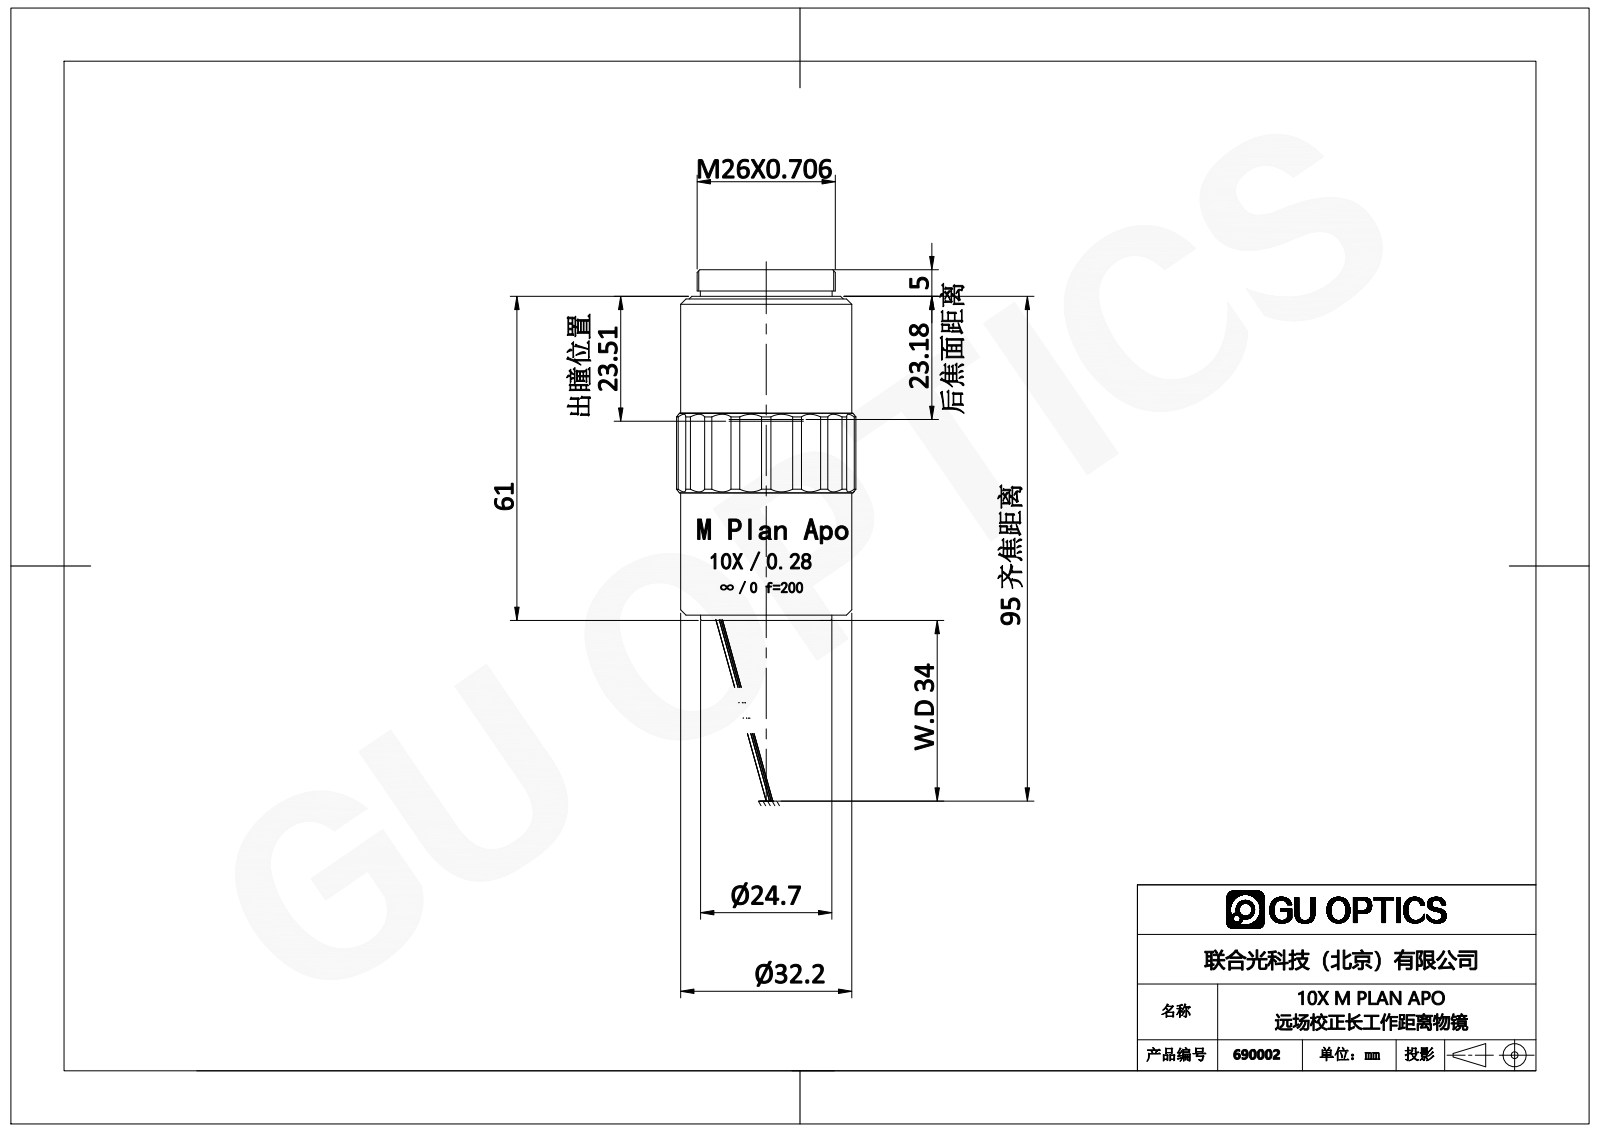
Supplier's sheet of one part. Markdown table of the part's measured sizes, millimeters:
| quantity | value |
| --- | --- |
| part name | 690002 |
| STEP written by | SolidWorks 2020 (CONFIG_CONTROL_DESIGN) |
| units | millimeters |
| bodies | 1 solid, 72 faces (8 planar, 50 cylindrical, 14 other) |
| overall size | 66 × 33.65 × 33.65 |
| volume | 52 743 mm³ |
| surface area | 8 238 mm² |
| round bosses / shafts (diameter × count) | 32.2 × 1, 26 × 1, 24.8 × 1, 24.7 × 1 |
| partial cylindrical surfaces (radius × count) | 9.96 × 20, 16.87 × 1 |
| main face-to-face distances | 66, 1, 65, 61, 60, 5, 60.5, 59.5, 0.5, 5.5 |
